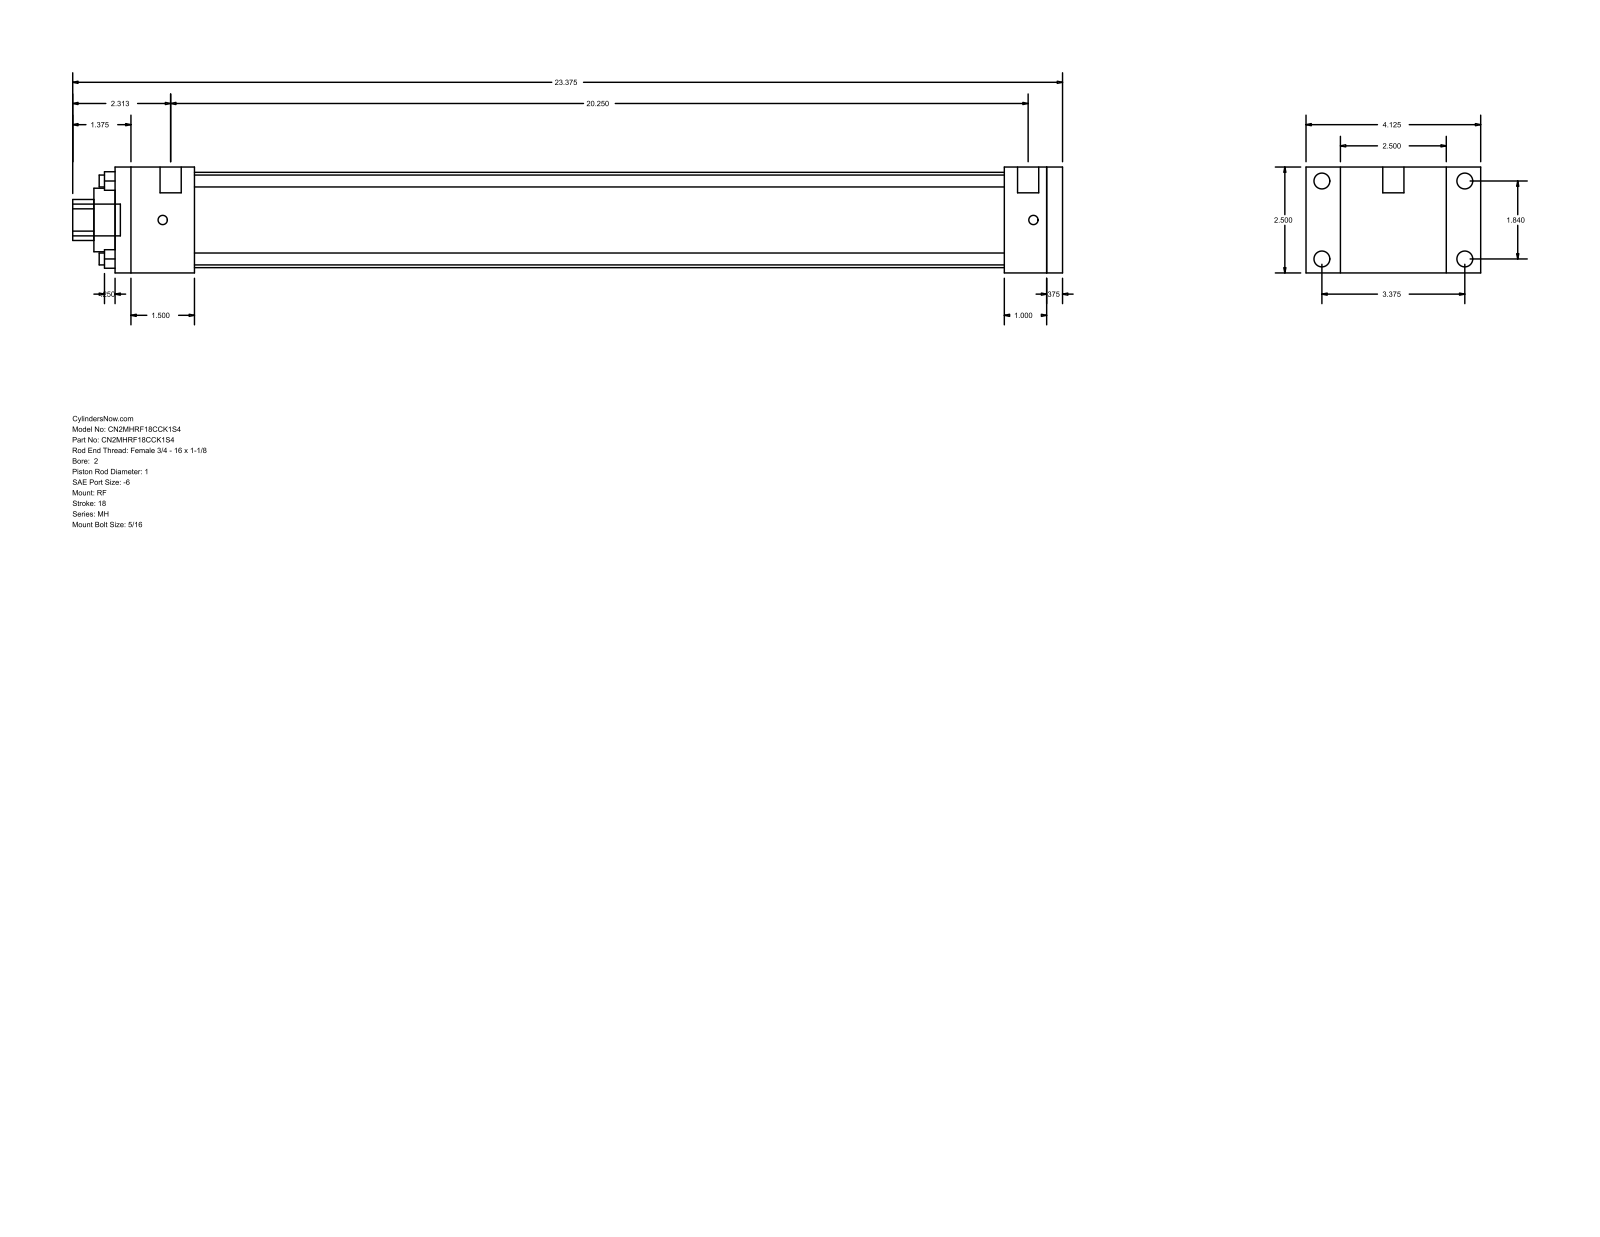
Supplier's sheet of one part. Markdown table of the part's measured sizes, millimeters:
| quantity | value |
| --- | --- |
| part name | MH_RF__0200_1 |
| STEP written by | GSSL Pune (CONFIG_CONTROL_DESIGN) |
| units | millimeters |
| bodies | 0 solids, 92 faces (64 planar, 28 cylindrical, 0 other) |
| overall size | 593.73 × 104.78 × 63.5 |
| round holes (diameter × count) | 7.14 × 4, 25.4 × 1, 38.1 × 1, 57.15 × 1 |
| round bosses / shafts (diameter × count) | 9.53 × 4, 5.56 × 4, 12.7 × 2, 19.05 × 1 |
| partial cylindrical surfaces (radius × count) | 12.29 × 1 |
| main face-to-face distances | 63.5, 568.33, 558.8, 9.53, 20.64, 25.4, 47.63, 533.4, 485.77, 511.17 |
| hole center spacings | 33.05, 46.74, 66.1 |
